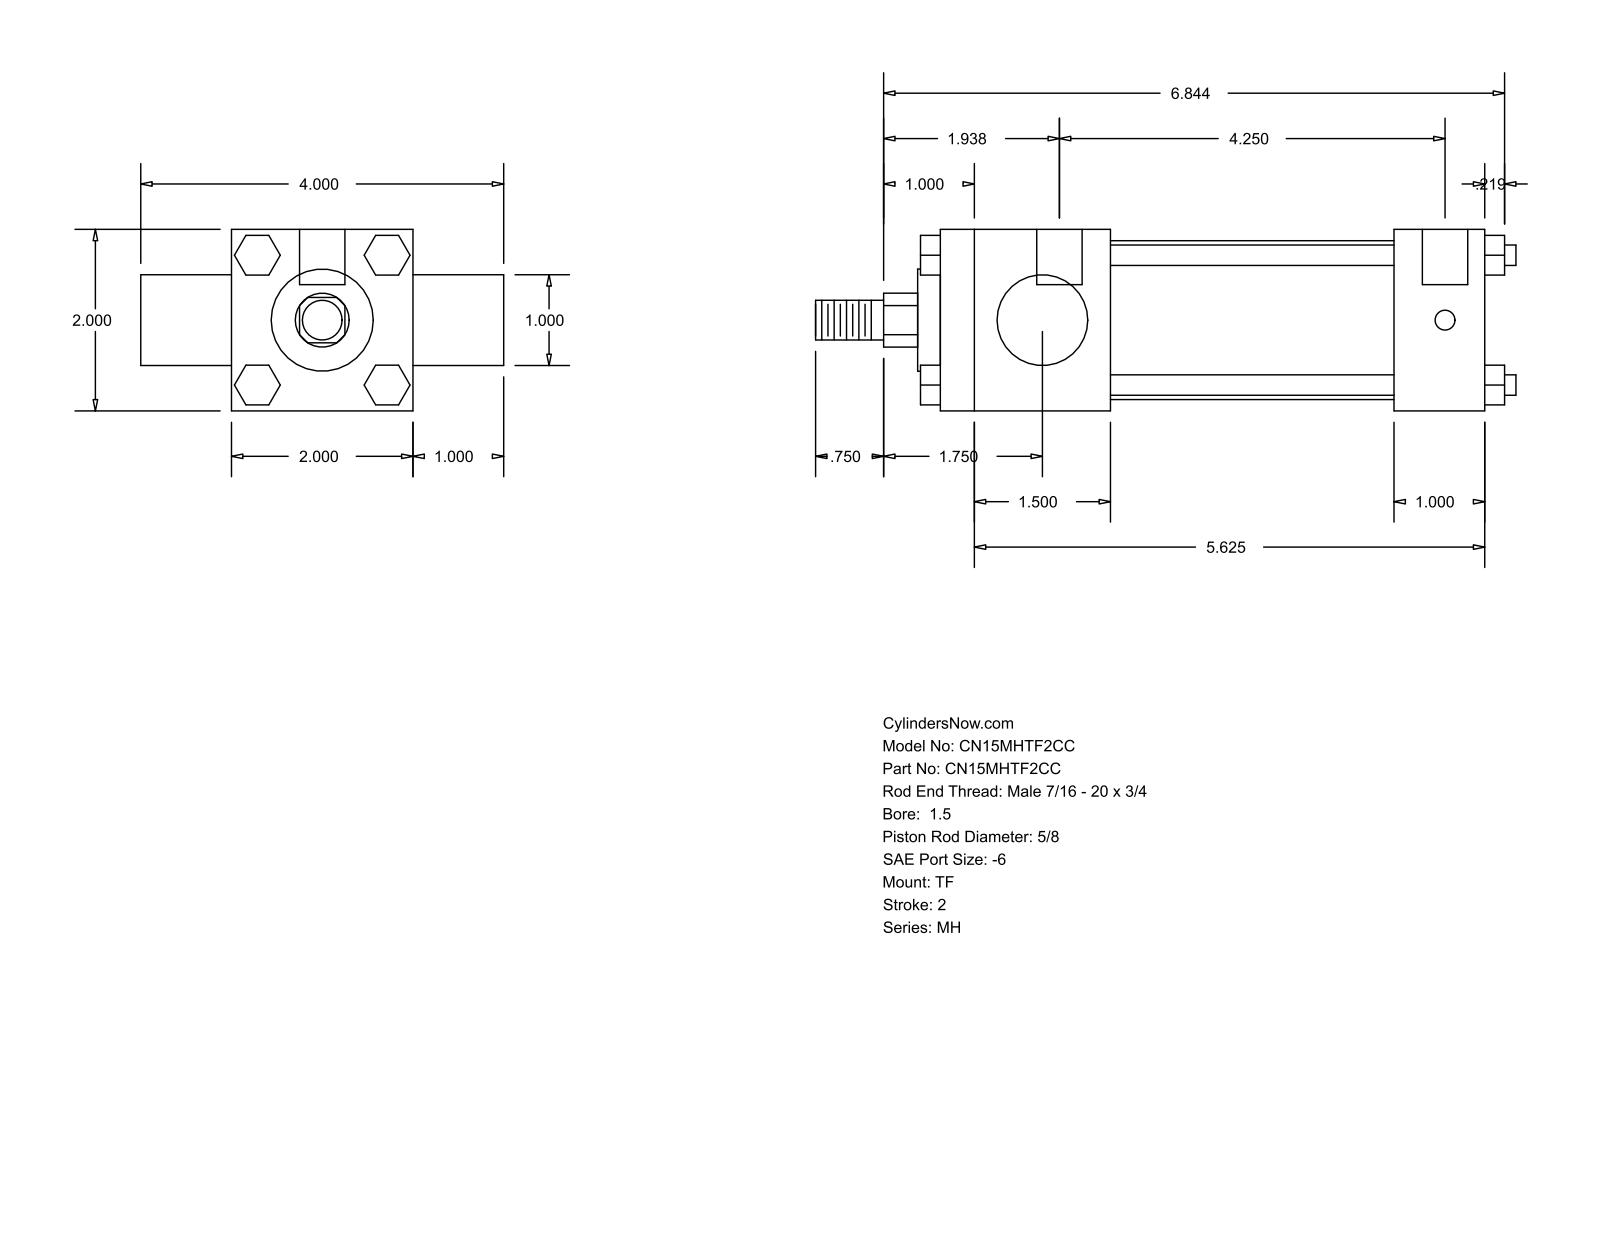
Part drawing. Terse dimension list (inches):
name: MH_TF__0150_0.625
written by: GSSL Pune (CONFIG_CONTROL_DESIGN)
unit: in
bodies: 0 solids, 120 faces (92 planar, 28 cylindrical, 0 other)
size: 7.719 × 4 × 2
holes: 3× ⌀0.219, 2× ⌀0.5
bosses: 4× ⌀0.225, 1× ⌀1.75, 1× ⌀1.125, 1× ⌀1, 1× ⌀0.625, 1× ⌀0.437
rounds: 1× R0.297
face distances: 2, 1, 6, 3, 1.875, 4.125, 5, 3.125, 0.437, 0.715
hole spacings: 0.125, 4.25, 4.375
